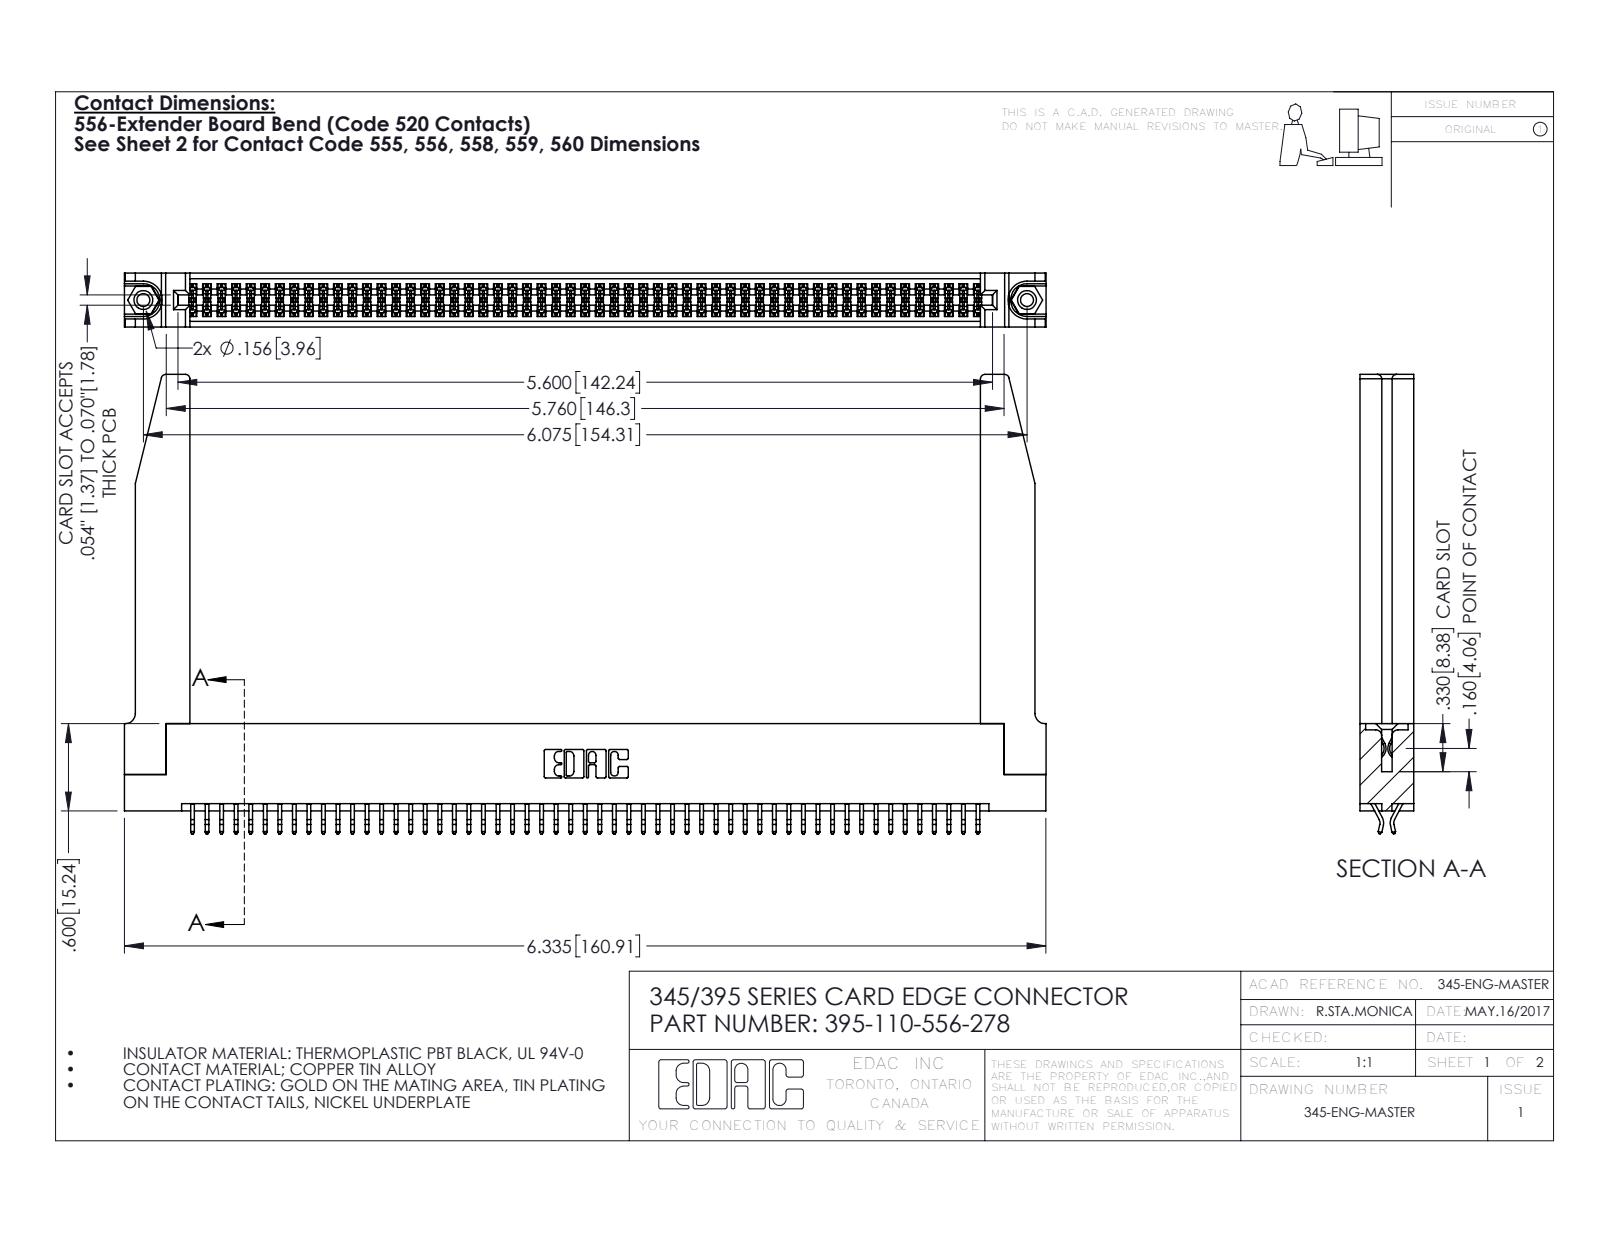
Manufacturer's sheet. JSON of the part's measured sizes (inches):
{"part_name": "345-250-001_345-250-001-102; 345-220-078_345-220-078; 345-292-001_556 Tail; 395-110-556-278 (+1 more)", "step_written_by": "SolidWorks 2016 (CONFIG_CONTROL_DESIGN)", "units": "inches", "bodies": {"solids": 115, "faces": 6520, "planar": 4292, "cylindrical": 2176, "other": 52}, "overall_size": [6.336, 3.157, 0.37], "volume_in3": 1.435, "surface_area_in2": 46.93, "round_holes": [[0.089, 2], [0.125, 2], [0.156, 2], [0.064, 1]], "round_bosses_or_shafts": [[0.155, 2]], "partial_cylinders_radius": [[0.006, 165], [0.01, 22], [0.03, 8], [0.007, 6], [0.031, 6], [0.026, 3], [0.01, 2], [0.014, 2]], "face_to_face_distances": [0.072, 0.37, 0.298, 0.2, 0.025, 0.098, 0.272, 0.225, 0.175, 0.148], "hole_center_spacings": [0.27, 5.839, 6.075]}
